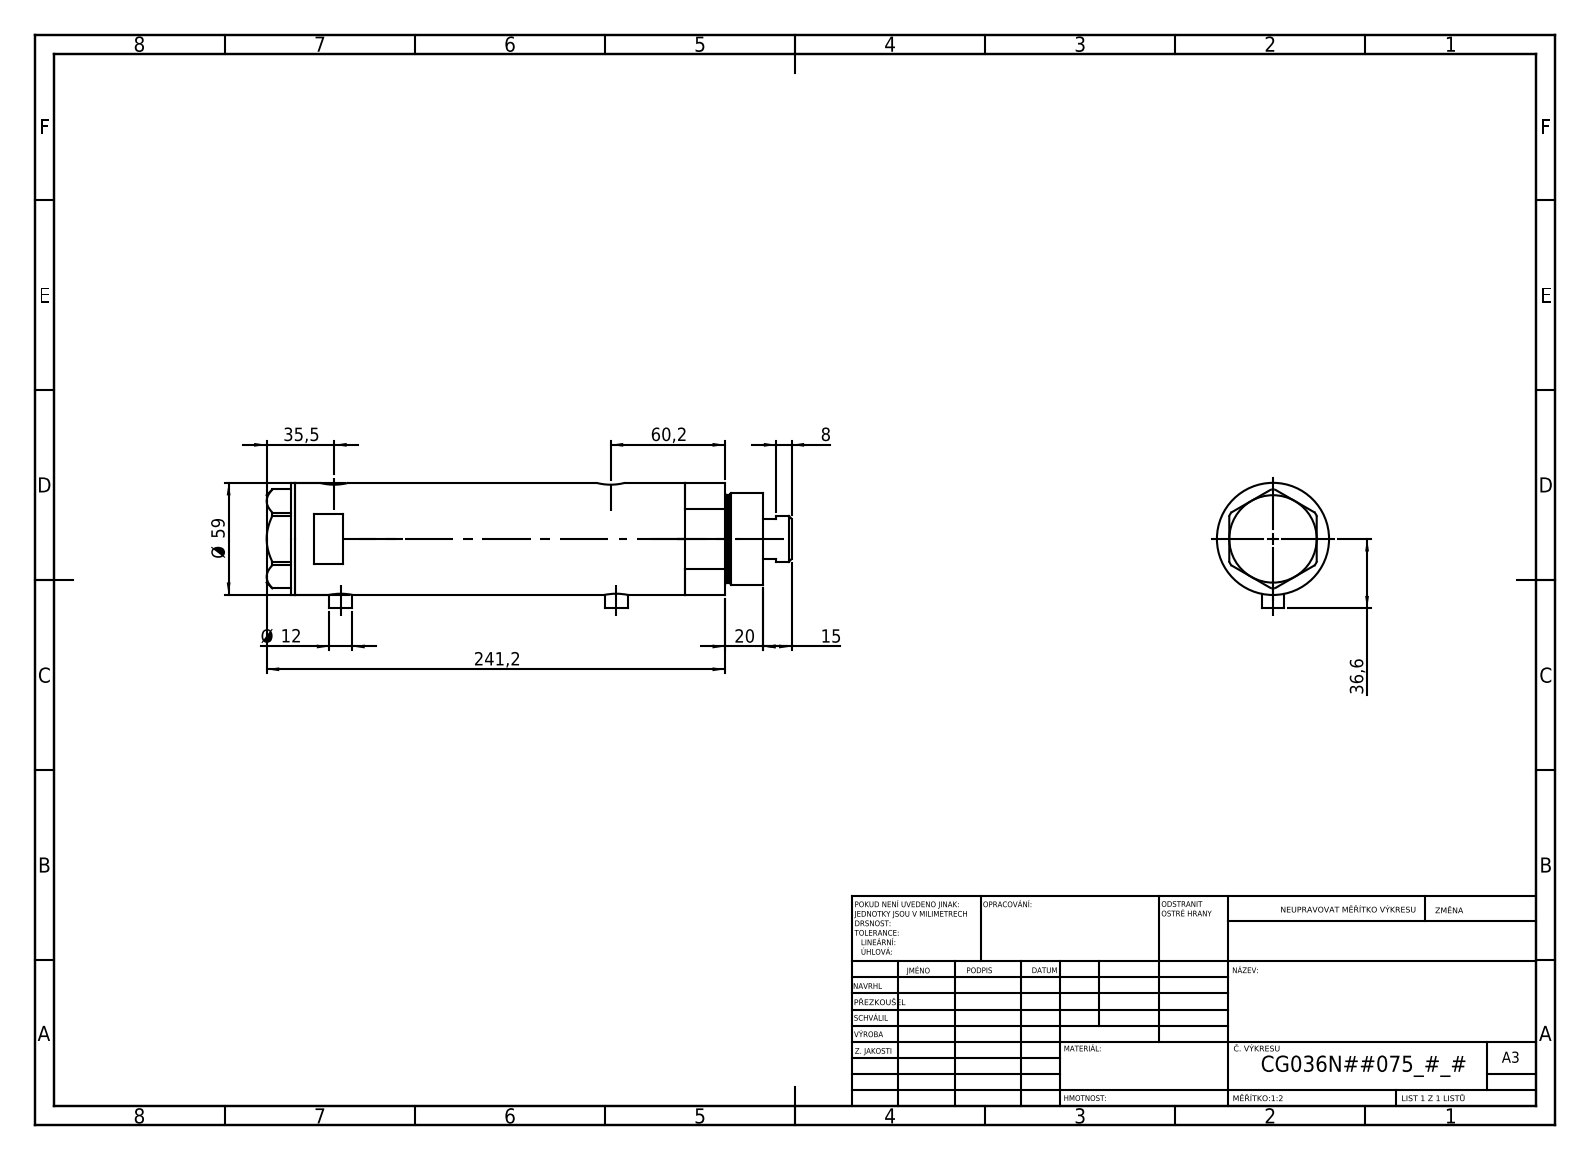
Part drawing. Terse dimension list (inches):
name: V270CG_BACK; V270CG_MIDDLE; V270CG_VC; V270CG_FRONT
written by: SolidWorks 2019 (CONFIG_CONTROL_DESIGN)
unit: in
bodies: 4 solids, 120 faces (51 planar, 49 cylindrical, 20 other)
size: 10.874 × 2.602 × 2.323
volume: 39.24 in³; area: 195.1 in²
holes: 2× ⌀0.383, 2× ⌀0.492, 2× ⌀0.591, 1× ⌀0.335, 1× ⌀0.984, 1× ⌀1.043, 1× ⌀1.417, 1× ⌀1.575, 1× ⌀2.047
bosses: 2× ⌀0.472, 1× ⌀2.323, 1× ⌀1.89, 1× ⌀1.811, 1× ⌀0.945
face distances: 6.583, 0.925, 5.657, 0.591, 1.516, 7.173, 0.079, 10.283, 9.693, 8.768
hole spacings: 0.114, 0.138, 5.591, 5.705, 5.728, 5.843
